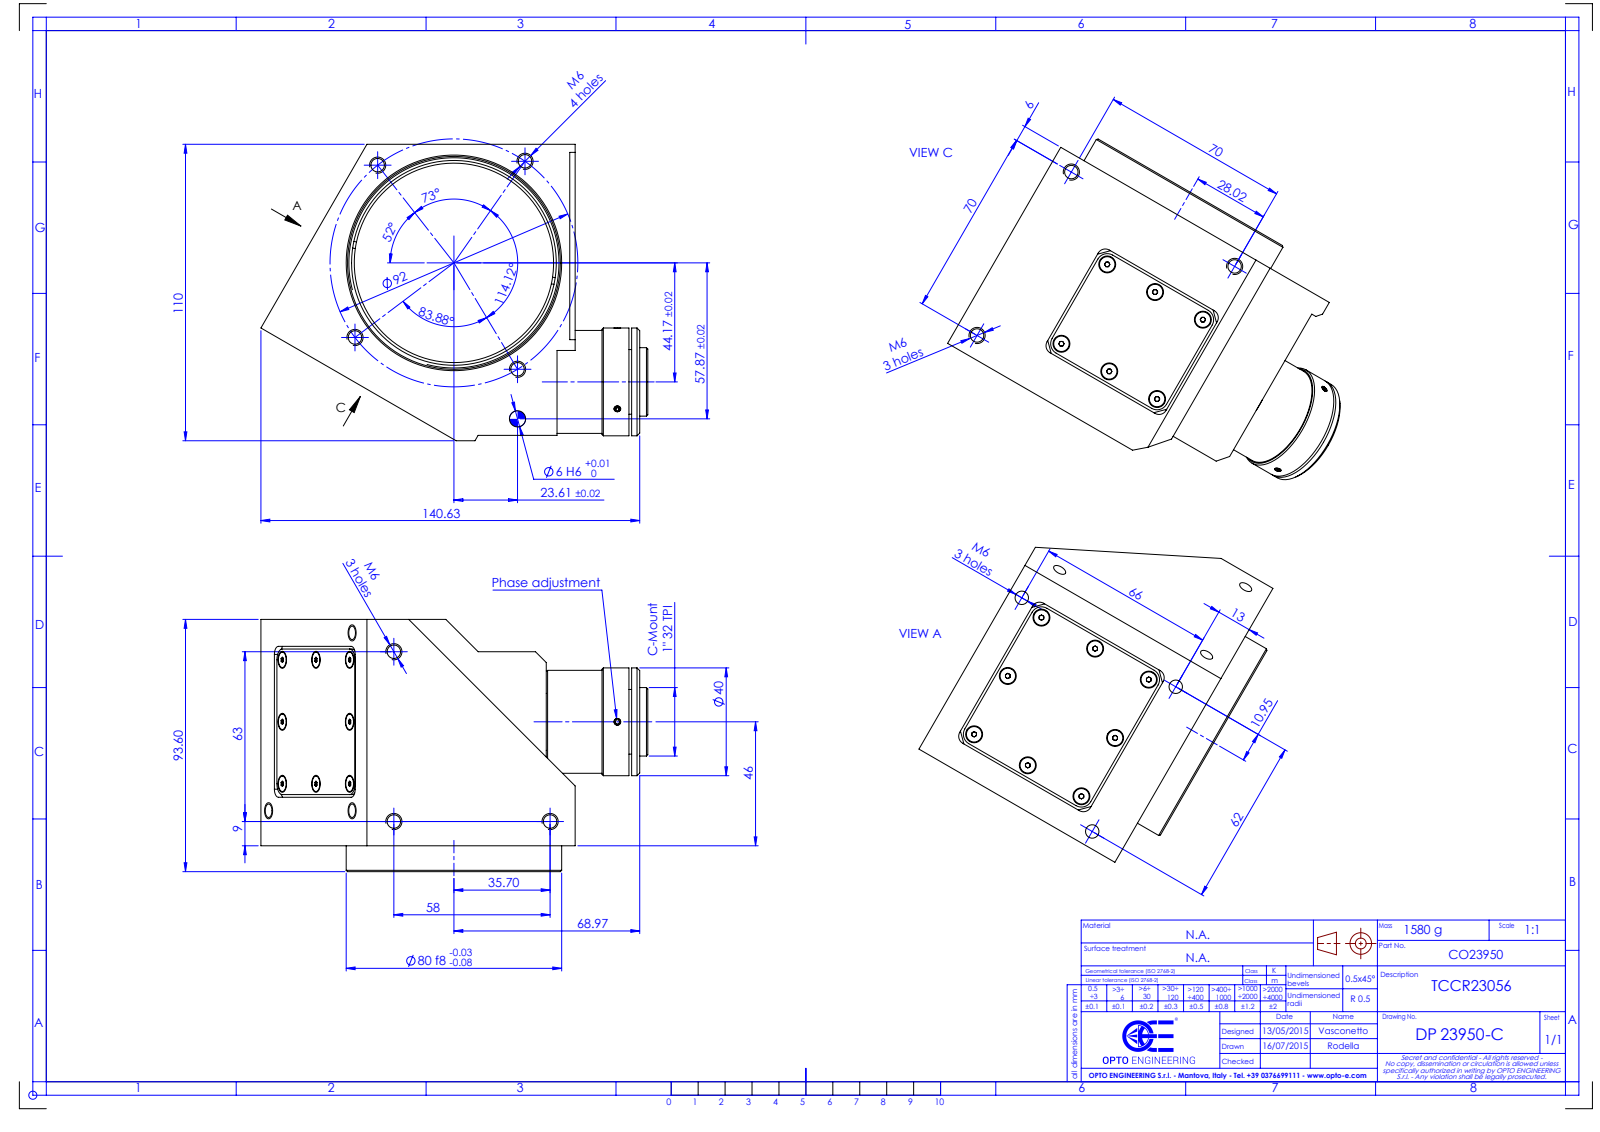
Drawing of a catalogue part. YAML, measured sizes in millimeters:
part_name: "DP23950_TCCR23056"
step_written_by: "SolidWorks 2021 (CONFIG_CONTROL_DESIGN)"
units: millimeters
bodies: {solids: 0, faces: 416, planar: 213, cylindrical: 105, other: 98}
overall_size: [143.63, 110, 93.6]
round_holes:
  - {diameter: 5, count: 13}
  - {diameter: 6, count: 1}
  - {diameter: 22, count: 1}
  - {diameter: 22.5, count: 1}
  - {diameter: 74, count: 1}
  - {diameter: 76, count: 1}
round_bosses_or_shafts:
  - {diameter: 5.75, count: 19}
  - {diameter: 80, count: 1}
  - {diameter: 40, count: 1}
  - {diameter: 38.2, count: 1}
  - {diameter: 37.8, count: 1}
  - {diameter: 25.4, count: 1}
partial_cylinders:
  - {radius: 4, count: 11}
  - {radius: 3, count: 8}
face_to_face_distances: [84, 0.51, 0.5, 2, 108, 1, 10.73, 72.5, 35.5, 4]
hole_center_spacings: [46, 70, 18.39, 54.72, 58, 61.49, 62.01, 62.5]
